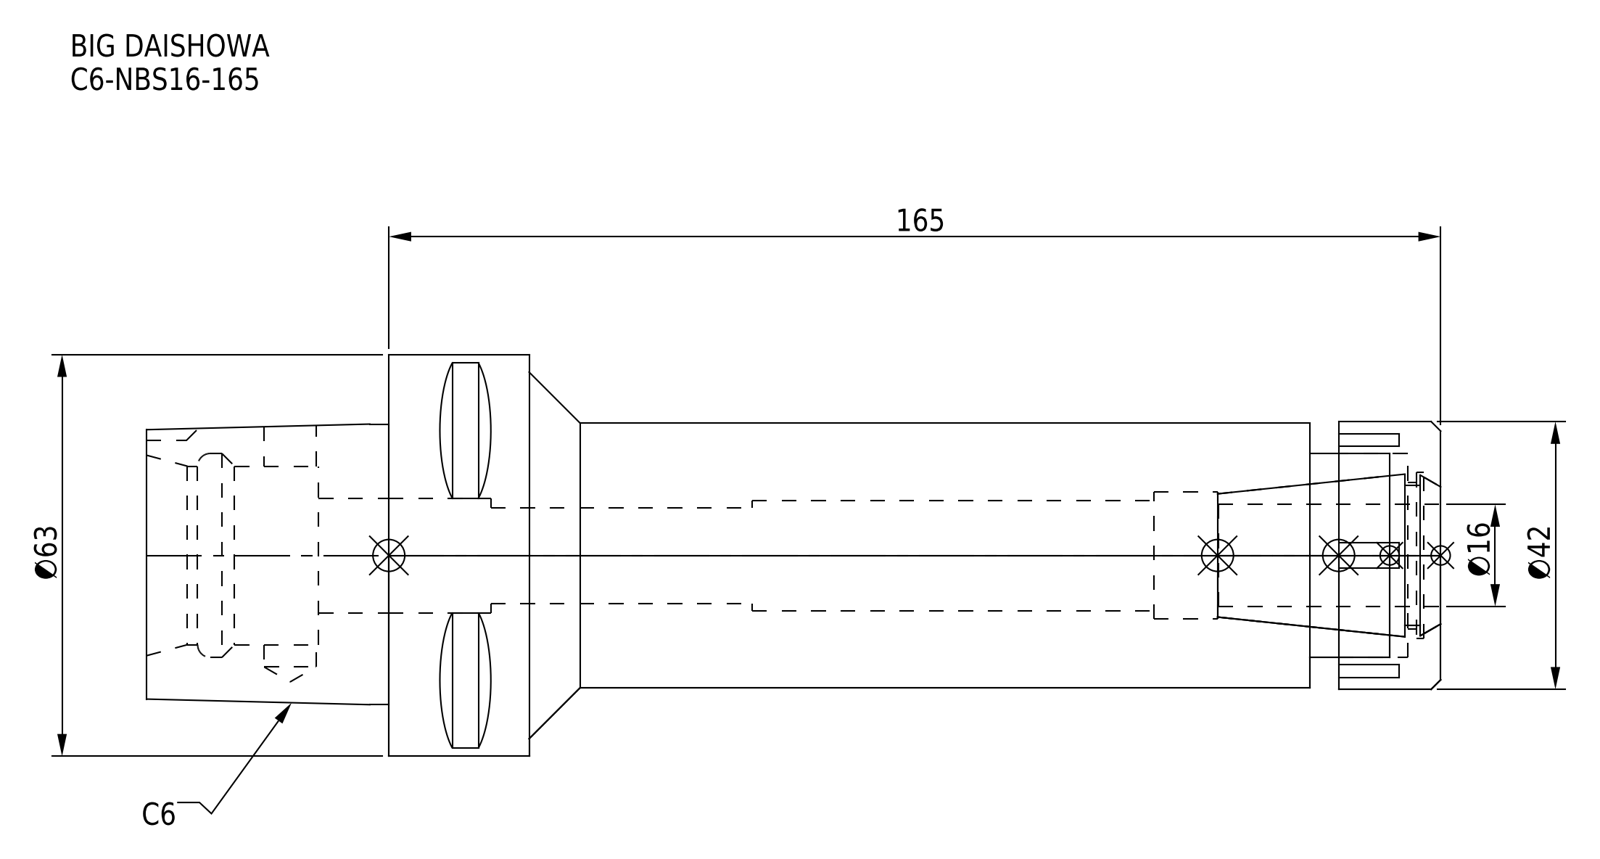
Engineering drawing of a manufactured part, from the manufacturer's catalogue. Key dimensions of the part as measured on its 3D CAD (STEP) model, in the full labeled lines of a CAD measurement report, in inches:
Part name (STEP PRODUCT): C6-NBS16-165.stp; DXF_TEMP_ASSY_ASM_4_ASM.stp; C6-NBS16-165; NBN16_1.stp (+3 more)
STEP written by: SolidWorks 2019 (CONFIG_CONTROL_DESIGN)
Units: inches
Bodies: 2 solids, 112 faces (61 planar, 33 cylindrical, 18 other)
Overall size (bounding box): 7.992 × 2.48 × 2.48
Volume: 15.37 in³ · Surface area: 77.72 in²
Round holes (diameter × count): ⌀0.319 ×1, ⌀0.591 ×1, ⌀0.681 ×1, ⌀0.709 ×1, ⌀0.787 ×1, ⌀0.906 ×1, ⌀1.024 ×1, ⌀1.102 ×1, ⌀1.26 ×1
Round bosses / shafts (diameter × count): ⌀2.48 ×1, ⌀1.654 ×1, ⌀1.634 ×1
Partial cylindrical surfaces — rounded edges, fillets, slot ends (radius × count): R0.197 ×1
Main face-to-face distances: 6.496, 0.315, 0.63, 5.866, 0.807, 5.689, 0.177, 5.63, 5, 4.823
